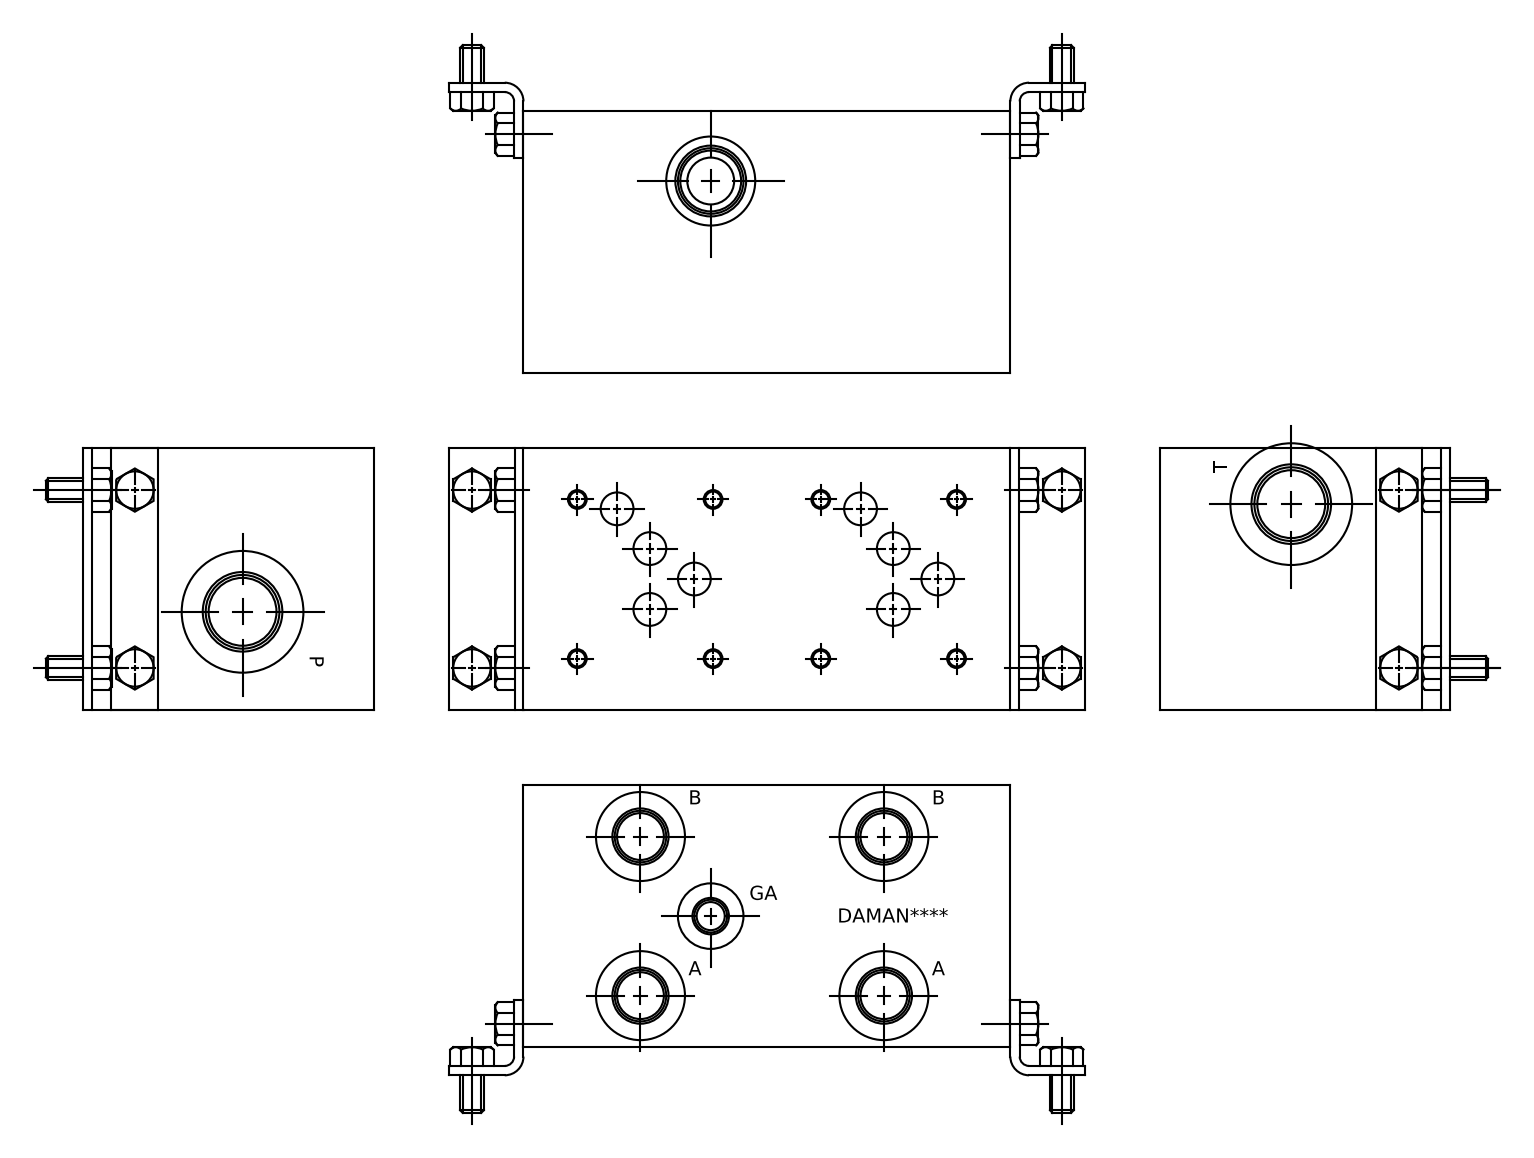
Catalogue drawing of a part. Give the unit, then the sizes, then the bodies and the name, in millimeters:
Units: millimetres
Overall size (bounding box): 165.1 × 88.9 × 88.9
Round holes (diameter × count): ⌀5.11 ×8, ⌀6.35 ×8, ⌀11.13 ×8, ⌀15.88 ×4, ⌀17.5 ×4, ⌀19.05 ×4, ⌀19.25 ×4, ⌀30.63 ×4, ⌀6.53 ×2, ⌀7.92 ×2, ⌀12.7 ×2, ⌀14.27 ×2
Main face-to-face distances: 88.9, 165.1, 0.79, 88.11, 164.31, 163.52, 19.05, 87.32, 1, 87.11
Hole centre spacings: 82.55, 53.97, 98.63, 46.05, 70.95, 13.88, 18.27, 20.62
Volume: 1 215 000 mm³ · Surface area: 94 769 mm²
Bodies: 1 solid, 645 faces (336 planar, 74 cylindrical, 235 other)
Part name (STEP PRODUCT): Part_AD05S023S~C_3D
STEP written by: Autodesk Inventor 2019 (AUTOMOTIVE_DESIGN)
